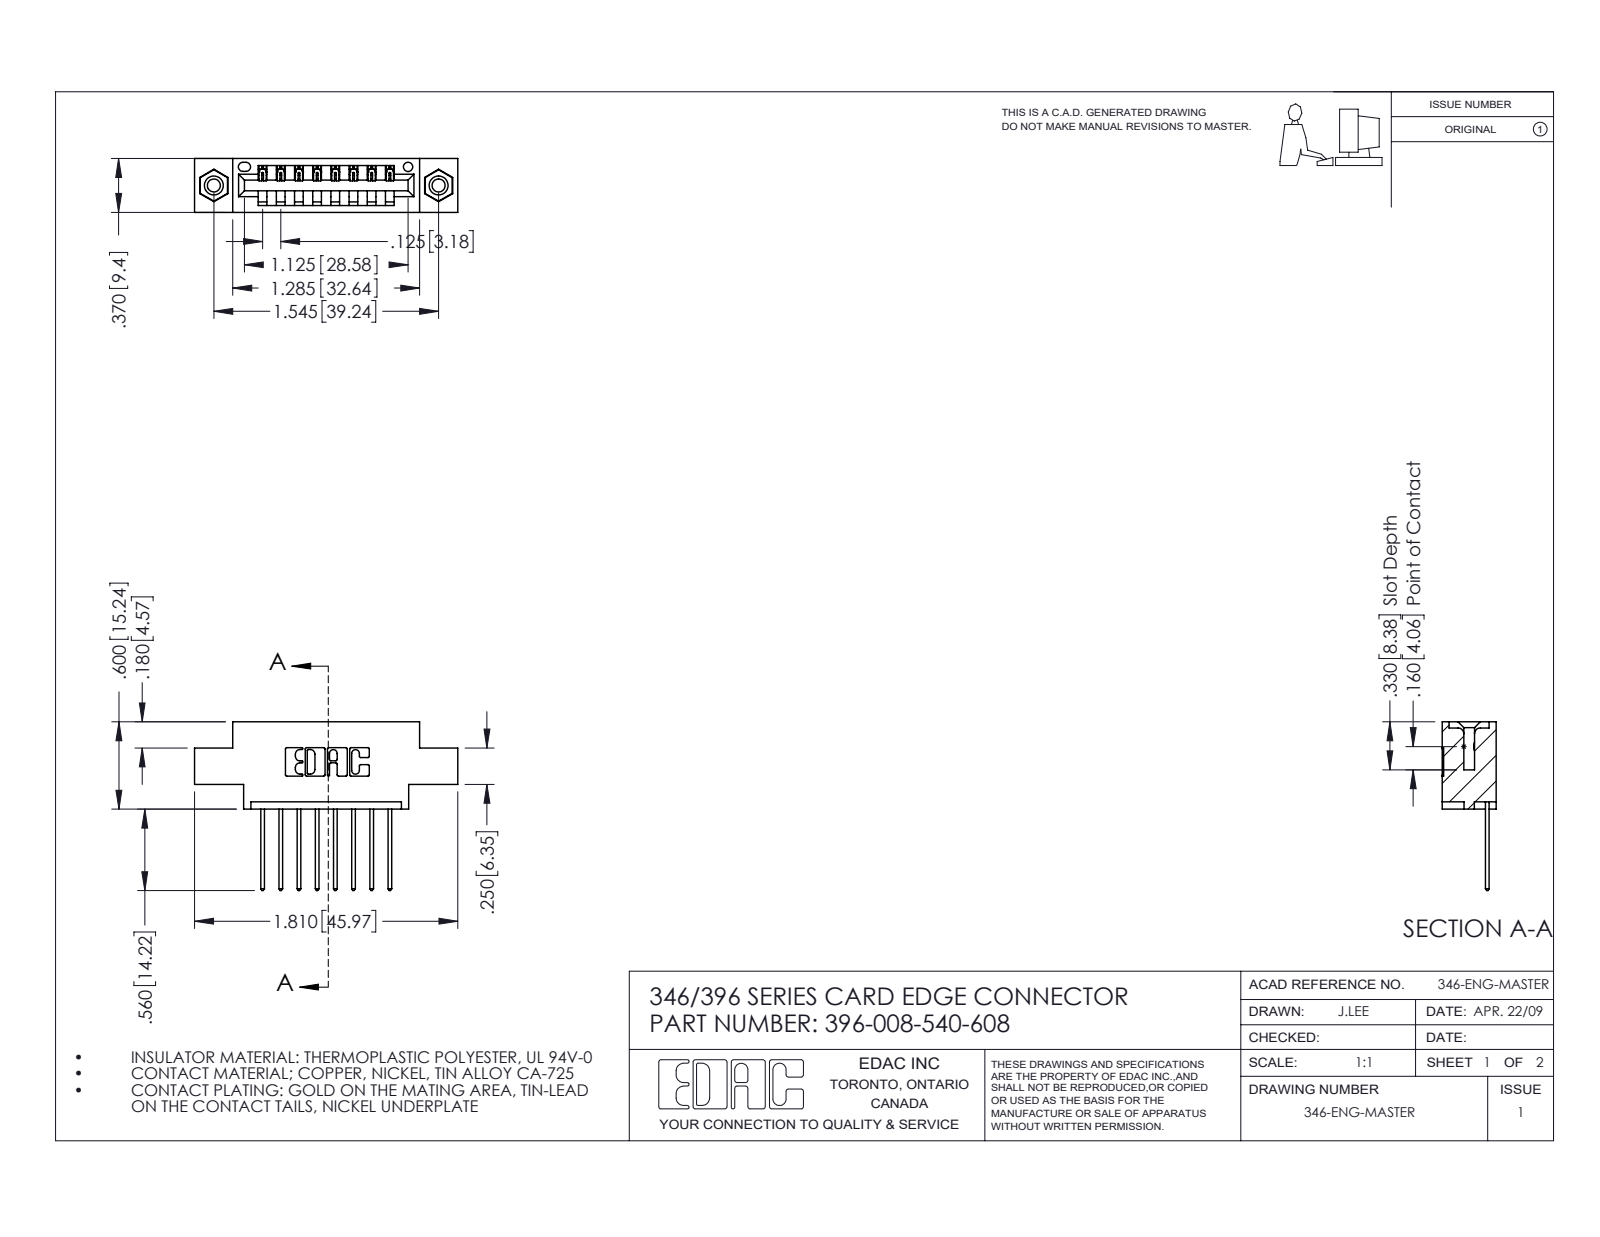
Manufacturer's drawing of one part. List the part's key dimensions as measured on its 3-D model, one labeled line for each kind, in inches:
Part name (STEP PRODUCT): 346 Part_0.170 Offset - 0.156 Dia-TI; 396-008-540-608; 345-250-001_345-250-003-102; 345-292-001_345-293-140
STEP written by: SolidWorks 2016 (CONFIG_CONTROL_DESIGN)
Units: inches
Bodies: 11 solids, 650 faces (432 planar, 202 cylindrical, 16 other)
Overall size (bounding box): 1.81 × 1.16 × 0.37
Volume: 0.245 in³ · Surface area: 7.617 in²
Round holes (diameter × count): ⌀0.089 ×2, ⌀0.125 ×2, ⌀0.156 ×2, ⌀0.064 ×1
Round bosses / shafts (diameter × count): ⌀0.155 ×2
Partial cylindrical surfaces — rounded edges, fillets, slot ends (radius × count): R0.01 ×22, R0.006 ×16, R0.01 ×16, R0.007 ×6, R0.031 ×6, R0.026 ×3, R0.031 ×2, R0.04 ×2
Main face-to-face distances: 0.25, 0.37, 0.048, 0.322, 0.072, 0.298, 0.025, 0.222, 0.148, 0.1
Hole centre spacings: 0.246, 1.341, 1.545
